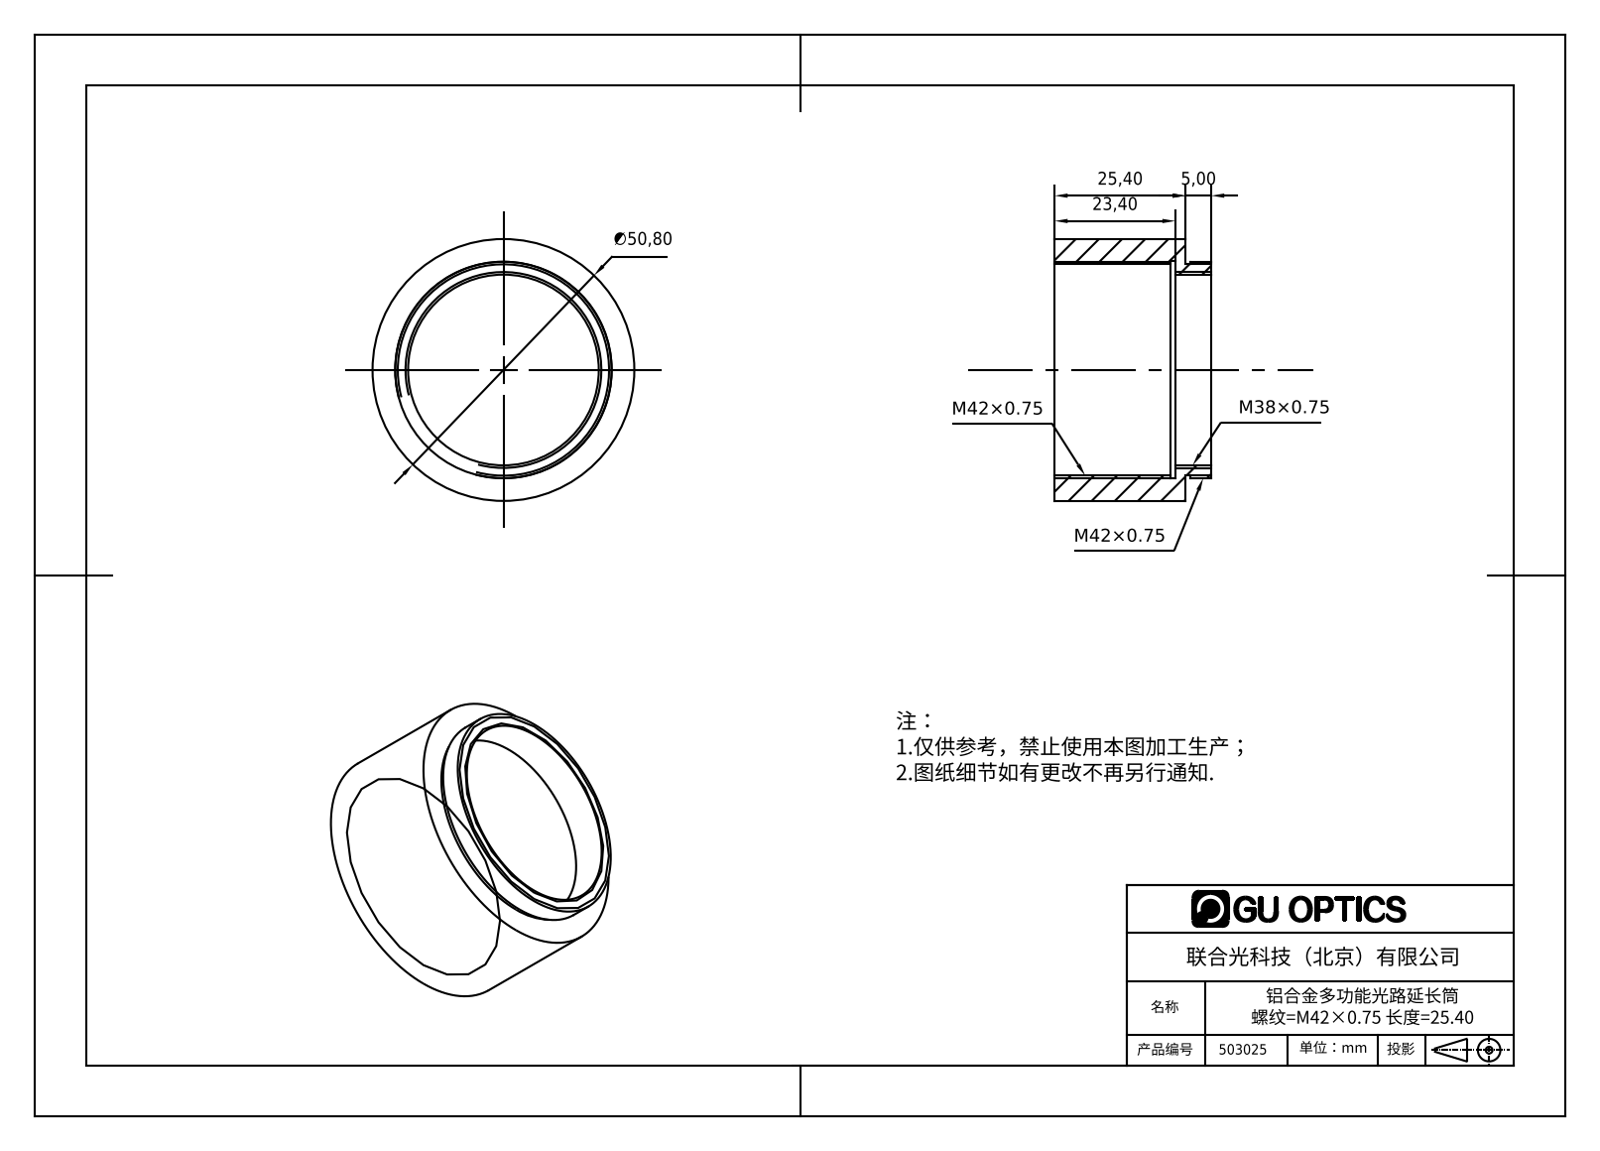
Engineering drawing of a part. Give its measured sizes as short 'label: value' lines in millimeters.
name: 503025
written by: SolidWorks 2016 (AUTOMOTIVE_DESIGN)
unit: mm
bodies: 1 solid, 18 faces (6 planar, 12 cylindrical, 0 other)
size: 50.8 × 50.8 × 30.4
volume: 19 845 mm³; area: 10 732 mm²
holes: 1× ⌀37, 1× ⌀41, 1× ⌀42.2
bosses: 1× ⌀50.8, 1× ⌀42
face distances: 25.4, 23.4, 2, 30.4, 7, 5, 1, 3, 4, 22.4
